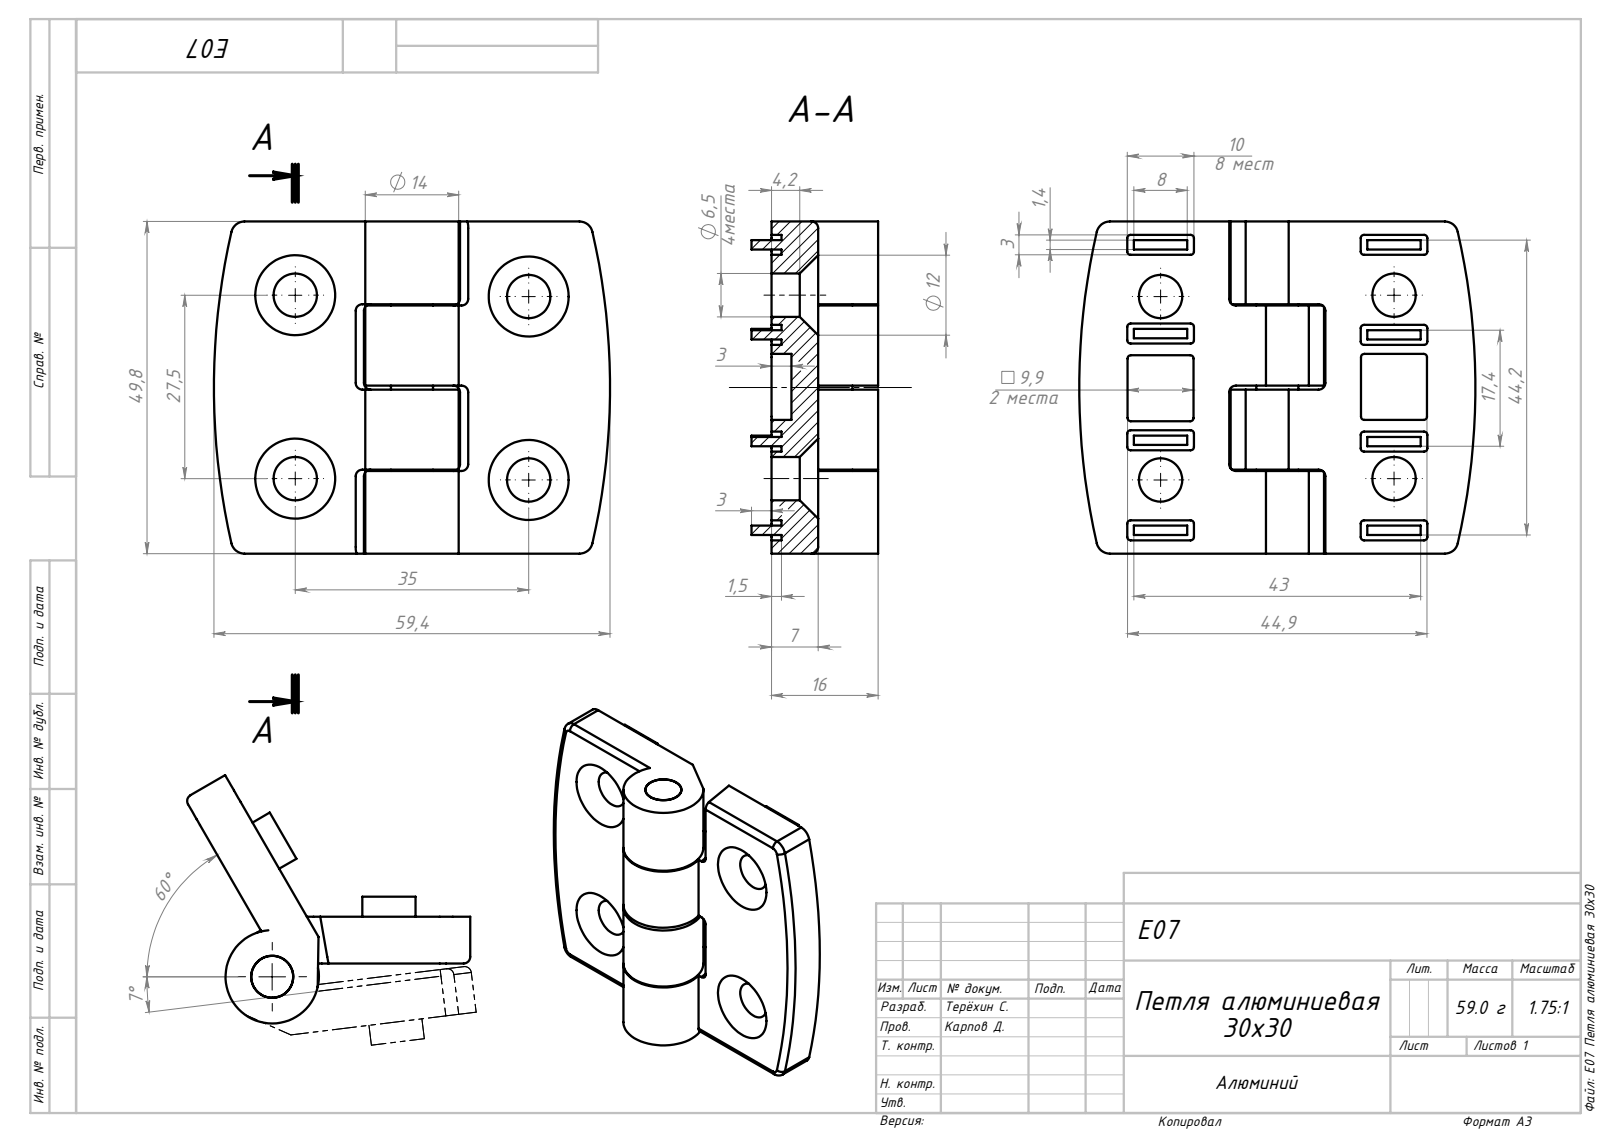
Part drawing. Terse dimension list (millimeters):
name: E07 Петля алюминиевая 3030; E07 Основание_00; E07 Палец_00
written by: SolidWorks 2019 (AUTOMOTIVE_DESIGN)
unit: mm
bodies: 3 solids, 216 faces (114 planar, 86 cylindrical, 16 other)
size: 59.42 × 49.8 × 19
volume: 21 659 mm³; area: 12 481 mm²
holes: 4× ⌀6.5, 1× ⌀6.3
rounds: 40× R0.5, 8× R1, 4× R2, 2× R104.83, 1× R7
face distances: 7, 12.6, 24.6, 49.8, 1.5, 25.2, 12.4, 37.4, 12.2, 12.8
hole spacings: 27.5, 35.02, 44.4, 44.65
